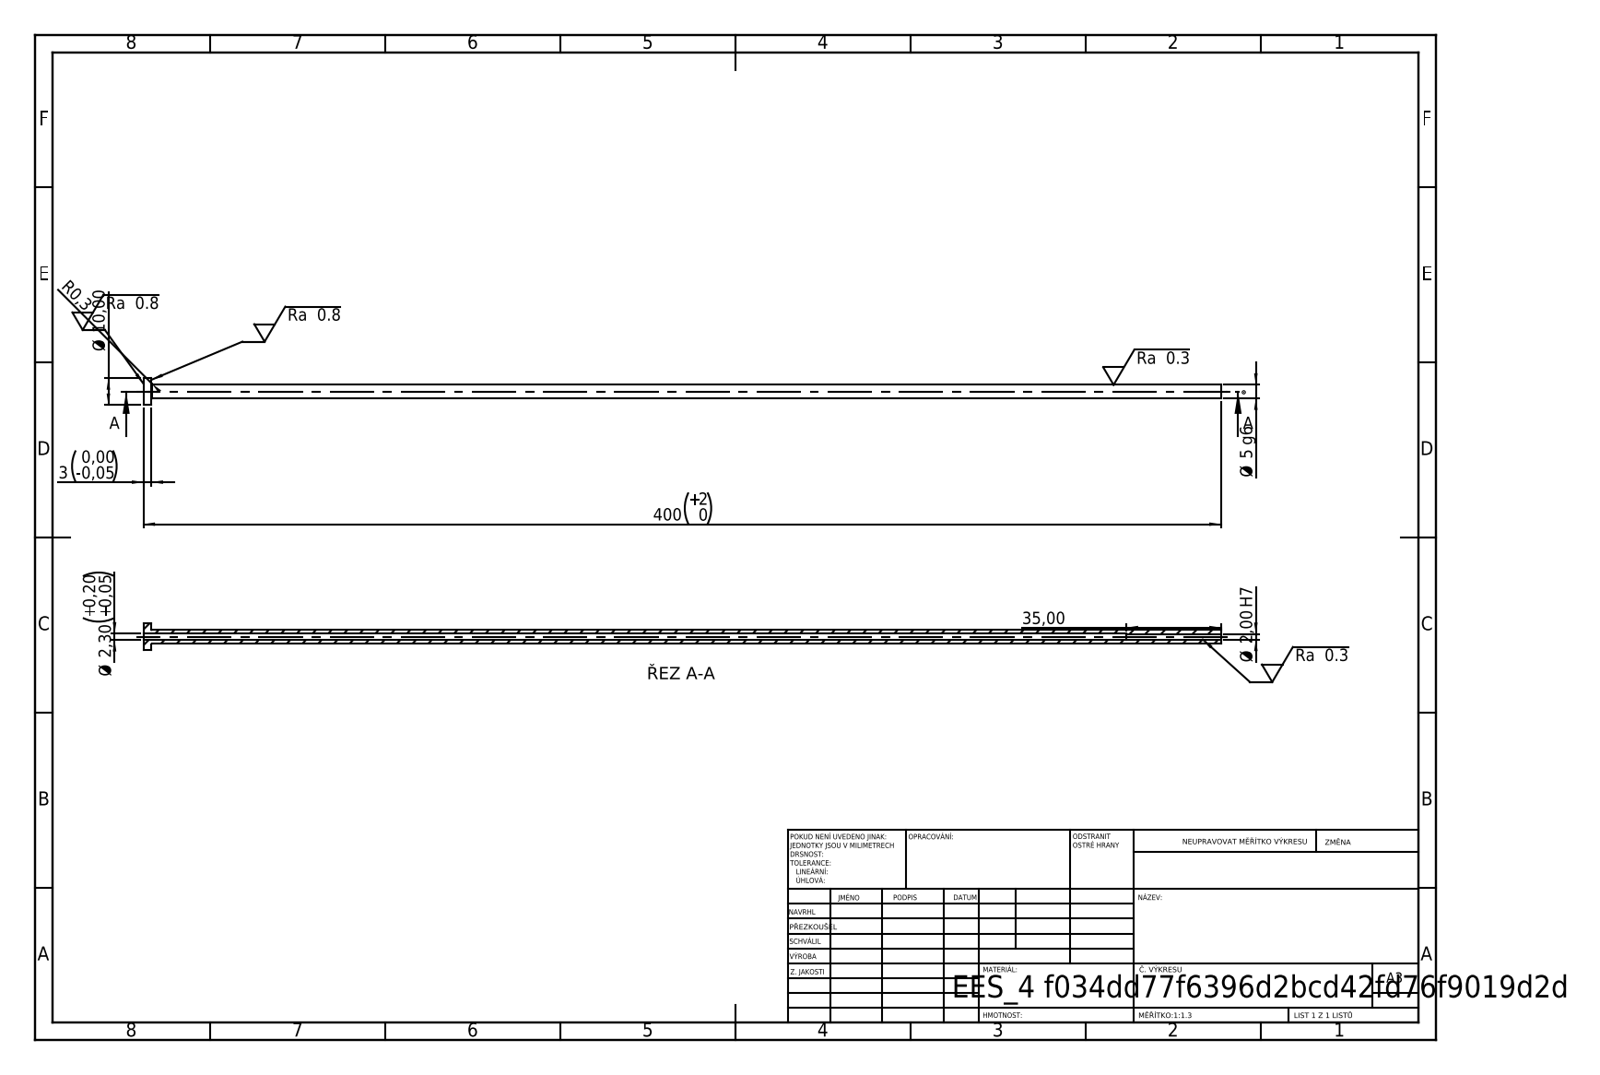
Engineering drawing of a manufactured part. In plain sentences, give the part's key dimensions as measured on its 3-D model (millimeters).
Its 3-D file was written by "SolidWorks 2019 (CONFIG_CONTROL_DESIGN)". It is 1 solid with 14 faces: 4 planar, 8 cylindrical and 2 other. Overall it measures 400 by 10 by 10 millimeters. Its volume is 6 405 cubic millimeters and its surface area 9 336 square millimeters. Round holes: 1 of diameter 2, 1 of diameter 2.3. Round bosses or shafts: 1 of diameter 10, 1 of diameter 5. The main face-to-face distances are 3, 400, 397, 365, 362, 35.
